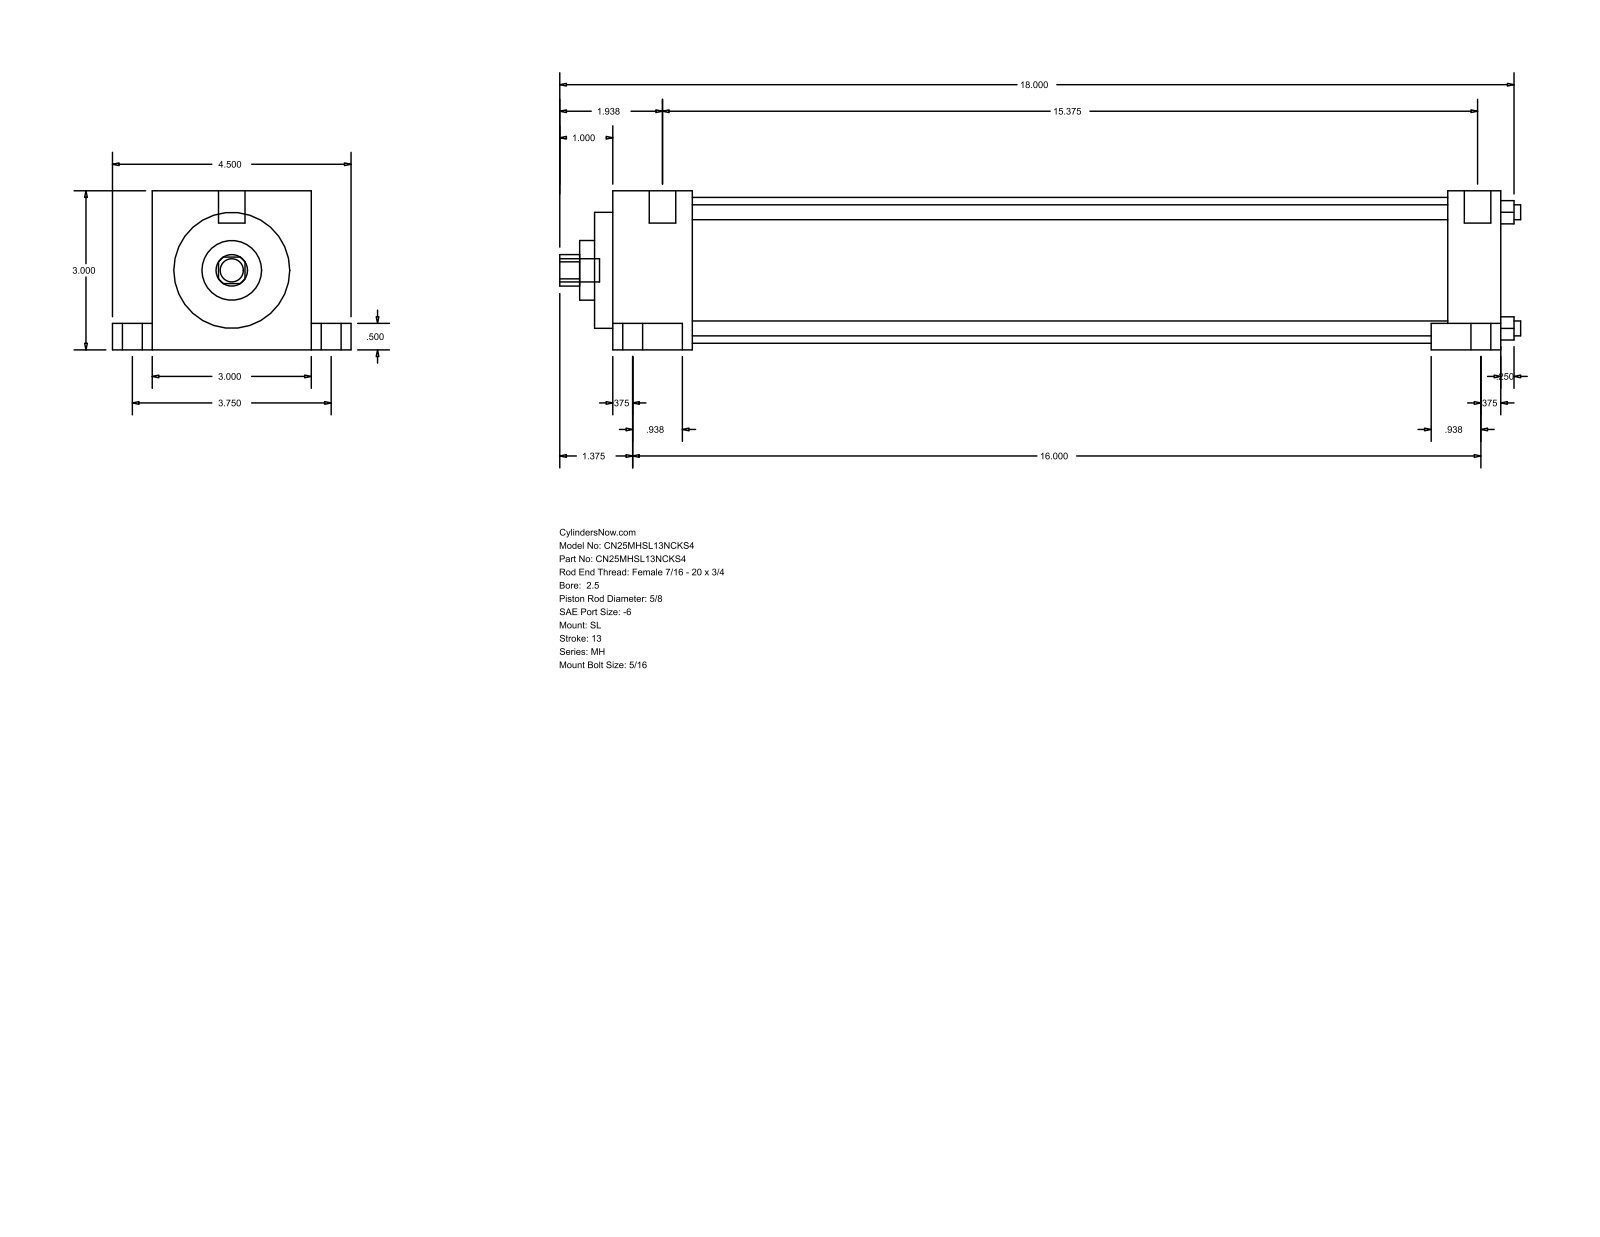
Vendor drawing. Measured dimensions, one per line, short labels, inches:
name: MH_SL__0250_0.625
written by: GSSL Pune (CONFIG_CONTROL_DESIGN)
unit: in
bodies: 0 solids, 86 faces (61 planar, 25 cylindrical, 0 other)
size: 18.125 × 4.5 × 3
holes: 4× ⌀0.281, 1× ⌀0.625, 1× ⌀1.125, 1× ⌀2.187, 1× ⌀2.75
bosses: 2× ⌀0.625, 2× ⌀0.375, 2× ⌀0.219, 1× ⌀0.5, 1× ⌀0.437
rounds: 1× R0.297
face distances: 3, 1, 16.094, 17.094, 0.5, 2.5, 0.75, 3.75, 1.25, 15.781
hole spacings: 1.548, 2.19, 3.097
